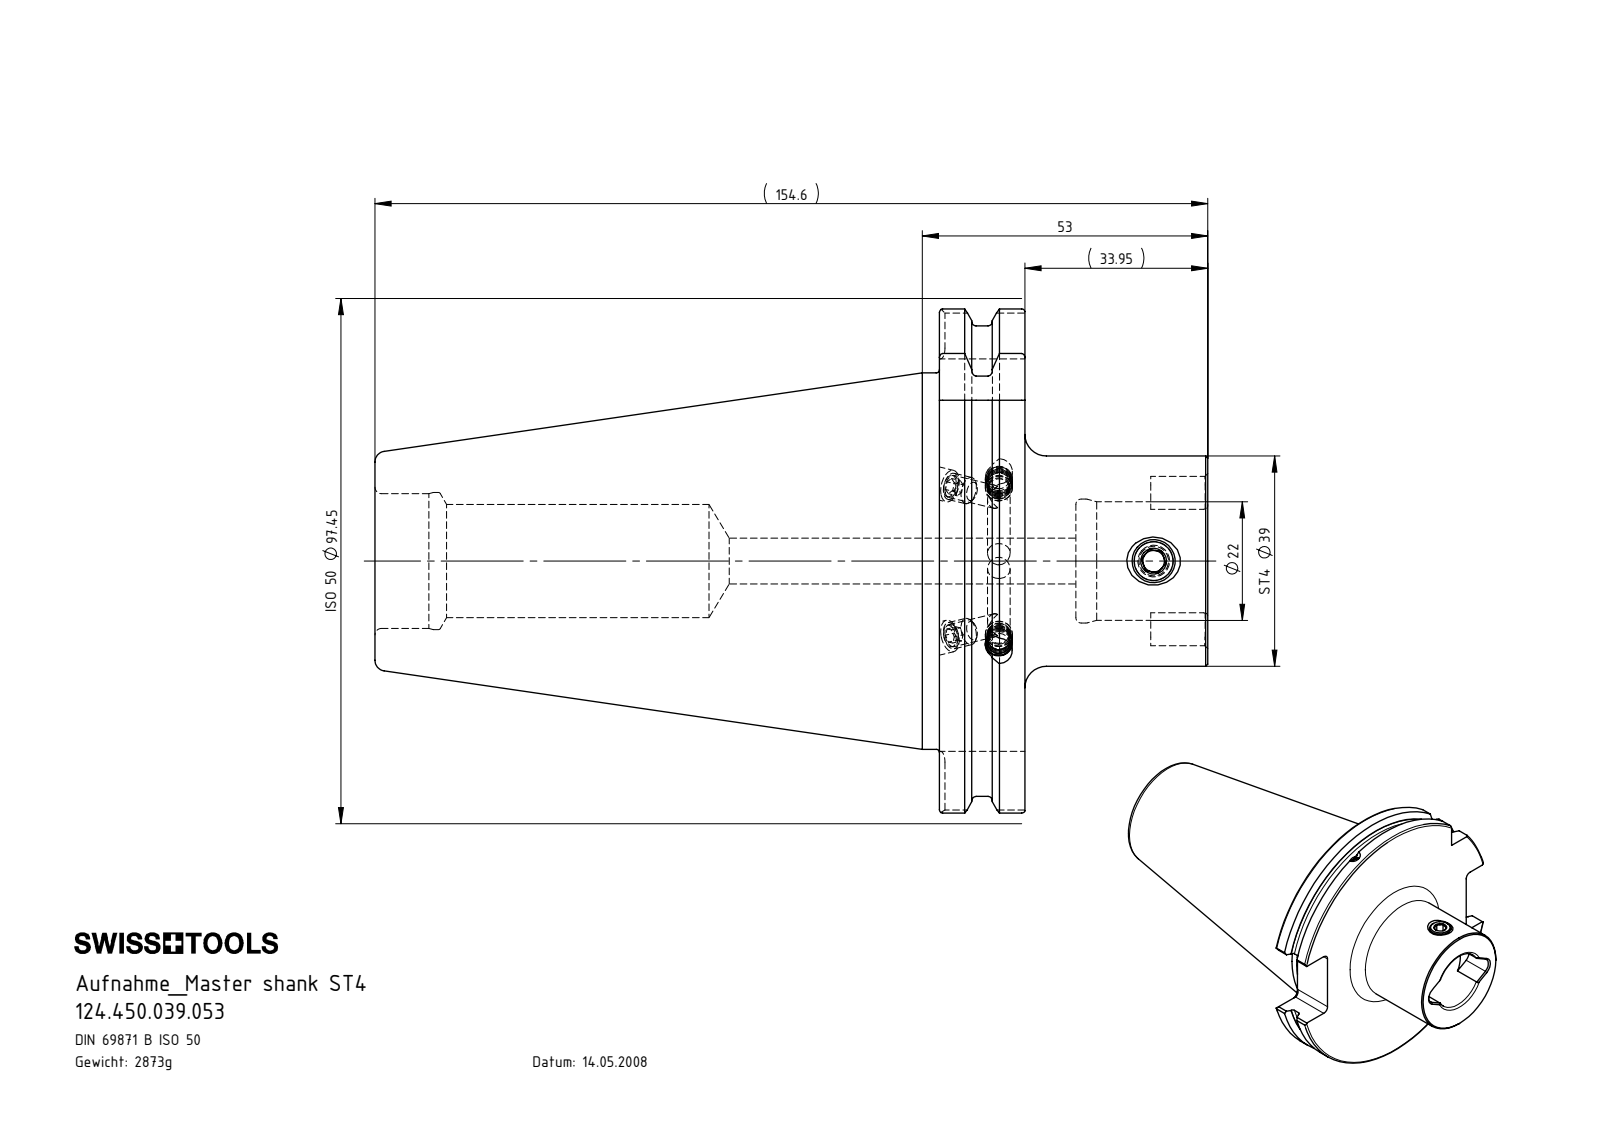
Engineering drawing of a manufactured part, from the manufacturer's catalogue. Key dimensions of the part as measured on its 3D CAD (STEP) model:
Part name (STEP PRODUCT): ISO 4026 - M5 x 5_PreviewCfg; SB5.ST4.K01.053; KVT_MB_600_050; ST4-ER1.001.011_A (+1 more)
STEP written by: SolidWorks 2017 (AUTOMOTIVE_DESIGN)
Units: millimetres
Bodies: 8 solids, 206 faces (78 planar, 46 cylindrical, 82 other)
Overall size (bounding box): 154.6 × 97.45 × 93.51
Volume: 366 015 mm³ · Surface area: 49 615 mm²
Round holes (diameter × count): ⌀4 ×3, ⌀4.2 ×3, ⌀6 ×2, ⌀5 ×1, ⌀7.25 ×1, ⌀8.5 ×1, ⌀21 ×1, ⌀22 ×1, ⌀23 ×1, ⌀25 ×1, ⌀25.45 ×1
Round bosses / shafts (diameter × count): ⌀5 ×3, ⌀91 ×1, ⌀69.85 ×1, ⌀39 ×1, ⌀8 ×1
Partial cylindrical surfaces — rounded edges, fillets, slot ends (radius × count): R2 ×8, R3.2 ×2, R48.73 ×1
Main face-to-face distances: 15.85, 49.8, 33.95, 104.8, 120.65, 154.6, 72.8, 130.1, 25.3, 9.45
